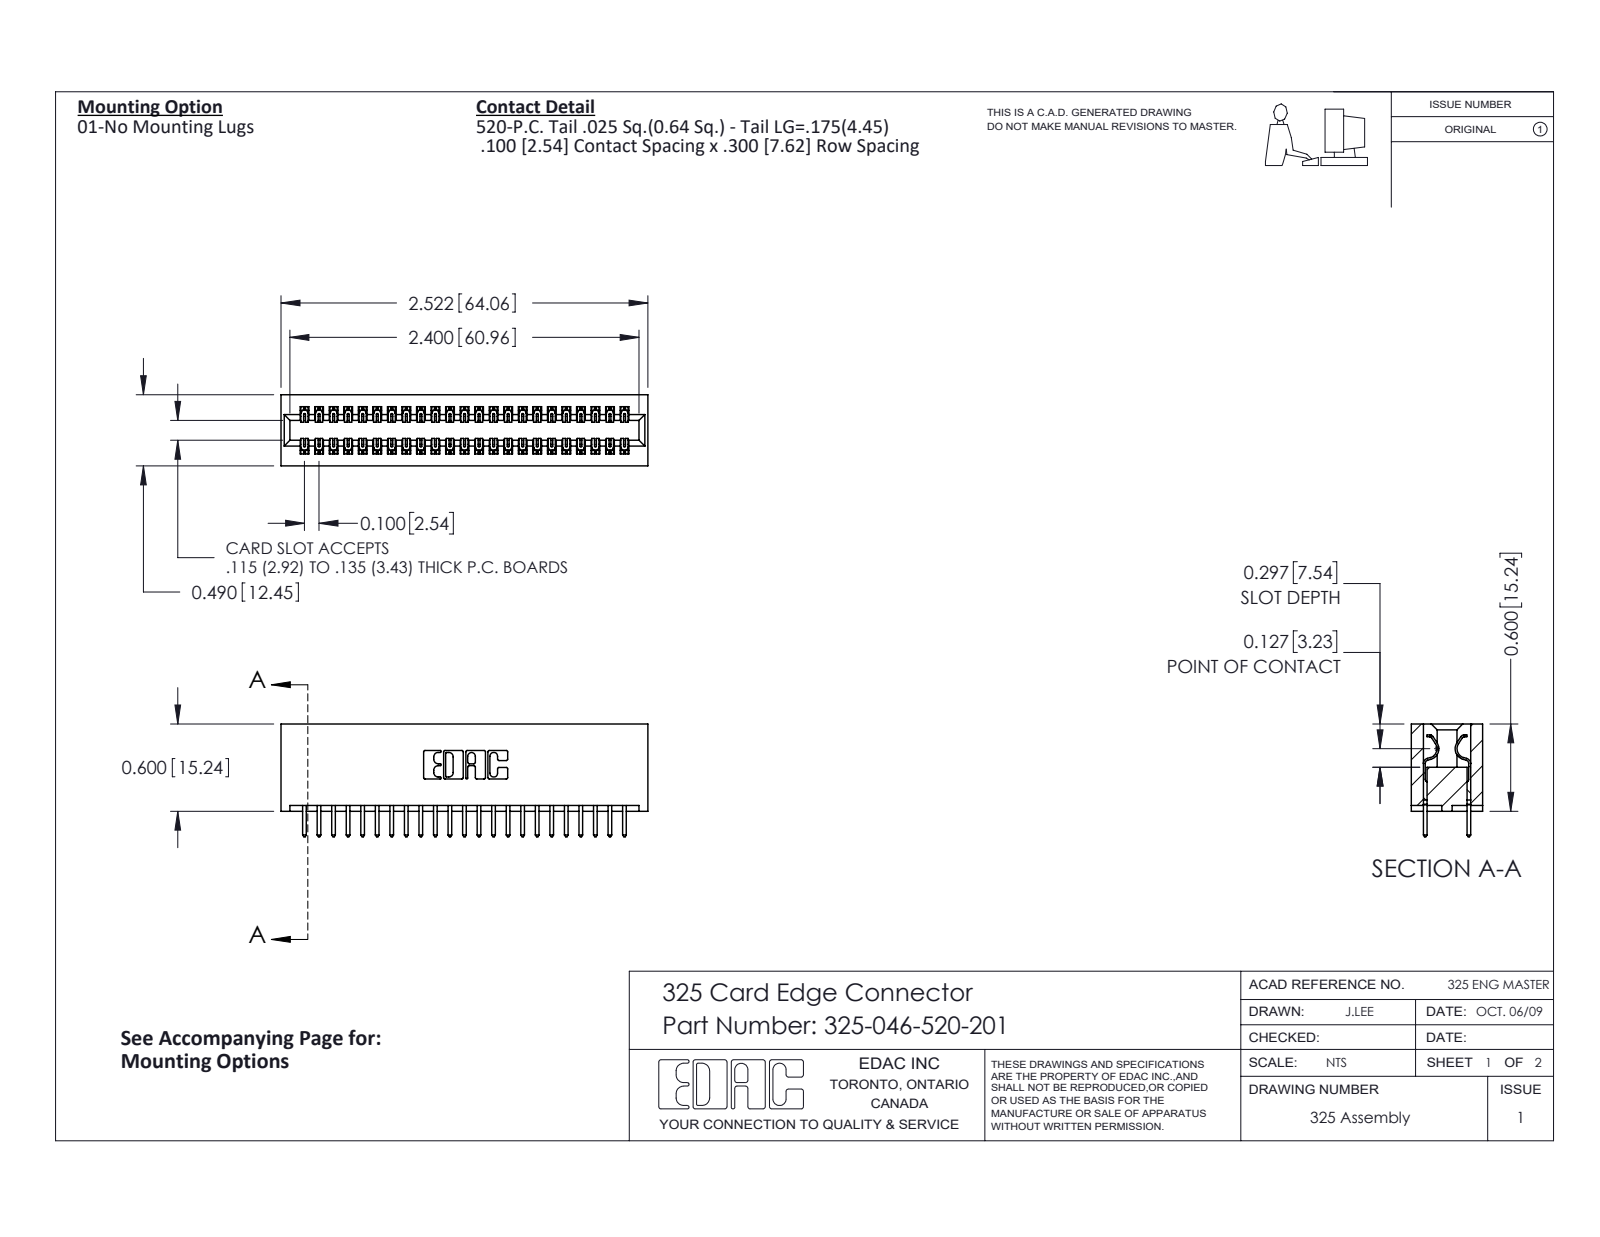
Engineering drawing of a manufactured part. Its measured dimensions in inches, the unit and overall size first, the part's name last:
Units: inches
Overall size (bounding box): 2.522 × 0.775 × 0.49
Partial cylindrical surfaces — rounded edges, fillets, slot ends (radius × count): R0.006 ×69, R0.01 ×46, R0.01 ×22, R0.007 ×6, R0.031 ×6, R0.026 ×3, R0.014 ×2, R0.022 ×2
Main face-to-face distances: 0.083, 0.407, 0.3, 0.49, 0.107, 0.383, 0.025, 0.325, 0.56, 0.1
Volume: 0.531 in³ · Surface area: 16.5 in²
Bodies: 47 solids, 2498 faces (1722 planar, 776 cylindrical, 0 other)
Part name (STEP PRODUCT): 325-292-001_325-293-120; 325 Part_Lugless; 325-046-520-201
STEP written by: SolidWorks 2016 (CONFIG_CONTROL_DESIGN)
